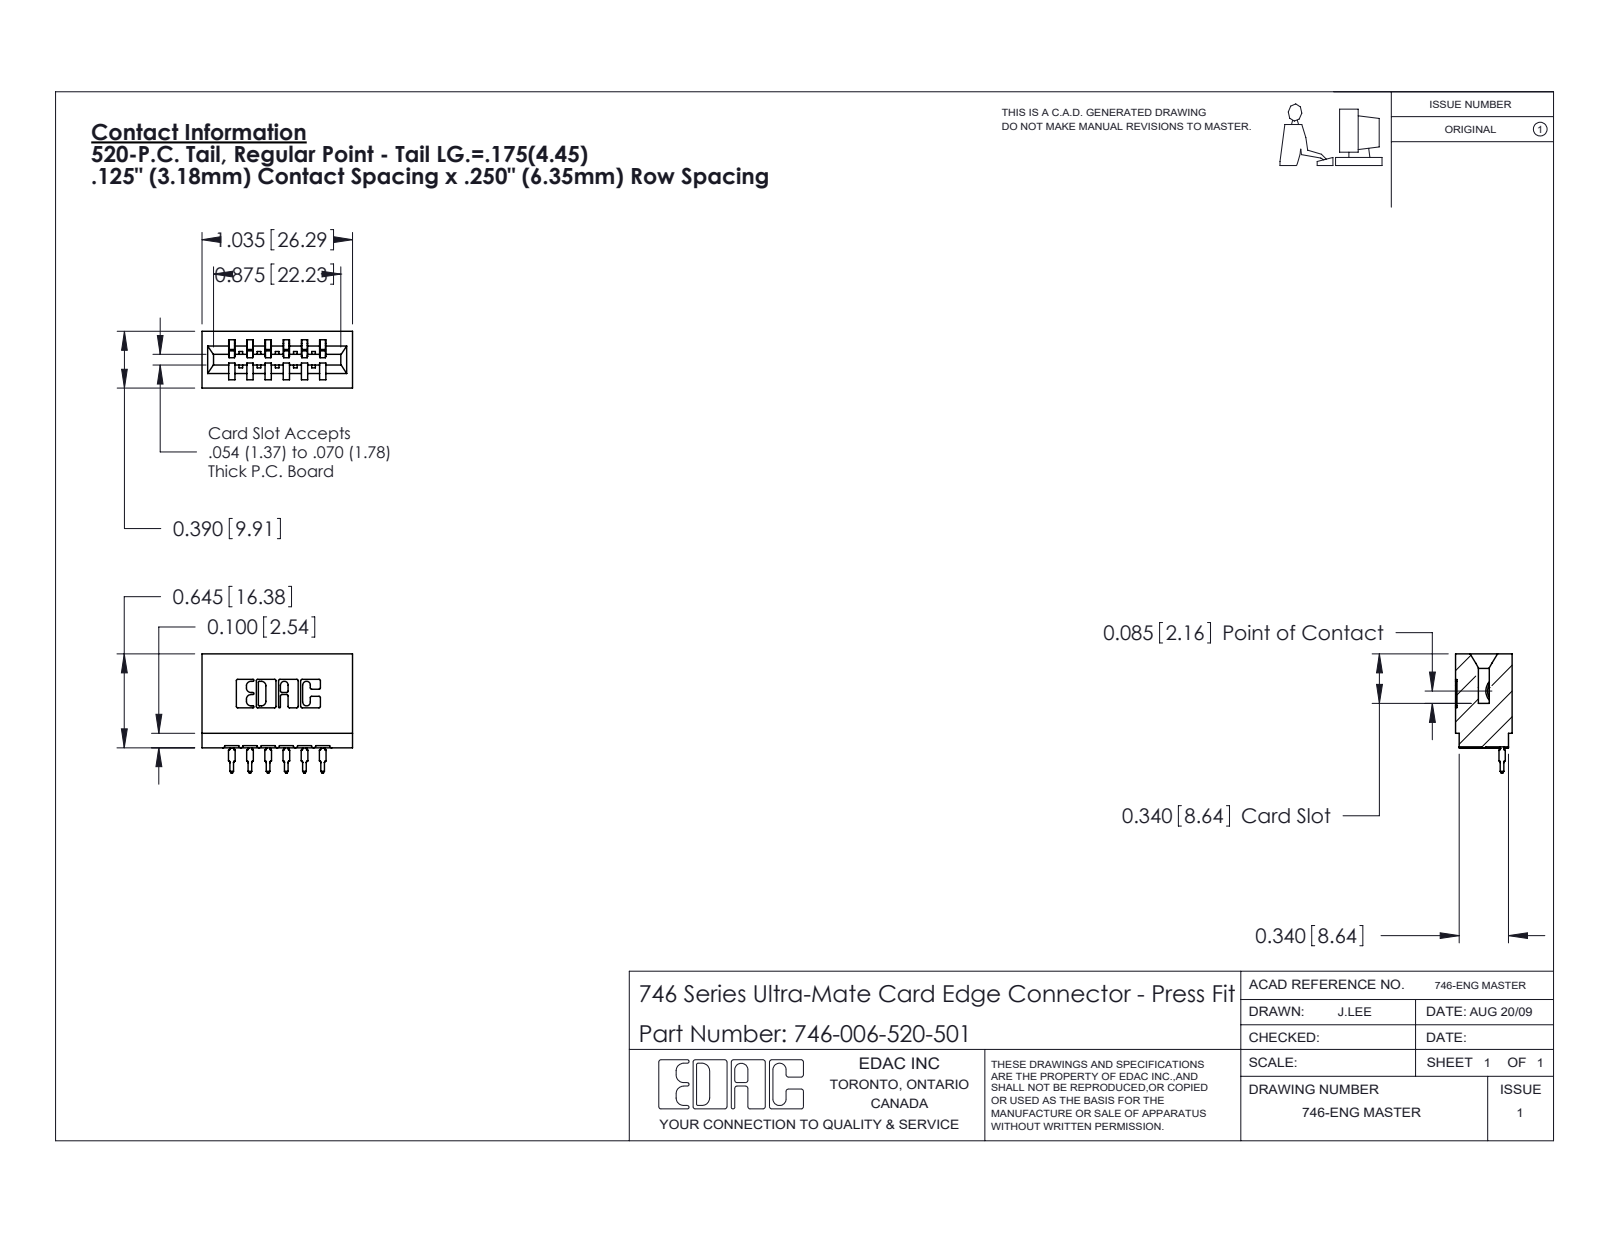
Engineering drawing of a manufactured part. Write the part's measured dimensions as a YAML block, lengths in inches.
part_name: "746 Part_.340 Slot Depth - 01; 746-292-001_520; 746-006-520-501"
step_written_by: "SolidWorks 2020 (CONFIG_CONTROL_DESIGN)"
units: inches
bodies: {solids: 7, faces: 745, planar: 433, cylindrical: 156, other: 156}
overall_size: [1.035, 0.819, 0.39]
volume: 0.193
surface_area: 5.69
partial_cylinders:
  - {radius: 0.01, count: 22}
  - {radius: 0.021, count: 12}
  - {radius: 0.015, count: 7}
  - {radius: 0.007, count: 6}
  - {radius: 0.031, count: 6}
  - {radius: 0.005, count: 4}
  - {radius: 0.011, count: 4}
  - {radius: 0.026, count: 3}
face_to_face_distances: [0.25, 0.125, 0.042, 0.333, 0.057, 0.125, 0.39, 0.292, 0.375, 0.5]
